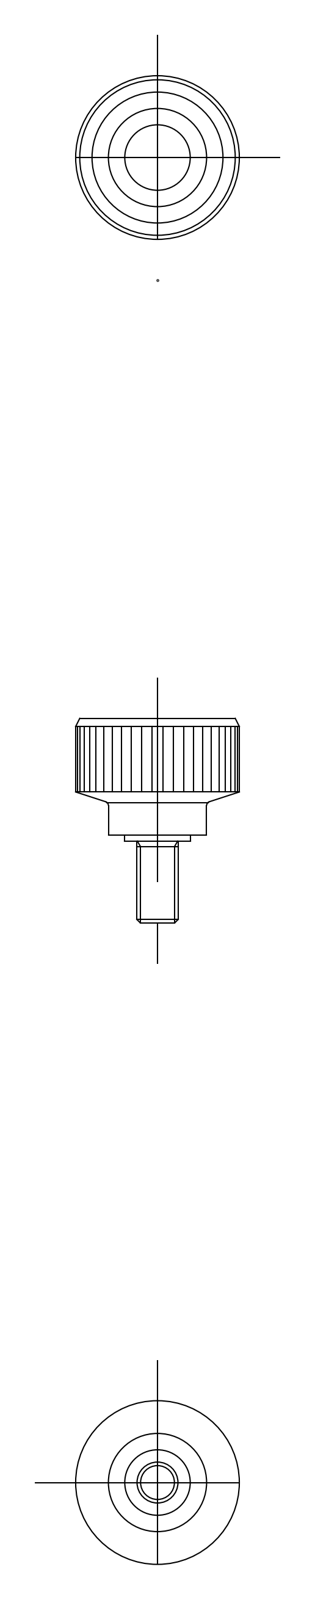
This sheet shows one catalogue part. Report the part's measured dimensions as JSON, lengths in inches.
{"part_name": "screw; knob; KKM_20_M5_10_4969_36", "step_written_by": "CADfix (AUTOMOTIVE_DESIGN)", "units": "inches", "bodies": {"solids": 2, "faces": 35, "planar": 0, "cylindrical": 0, "other": 35}, "overall_size": [0.984, 0.787, 0.787], "volume_in3": 0.18, "surface_area_in2": 3.24}
